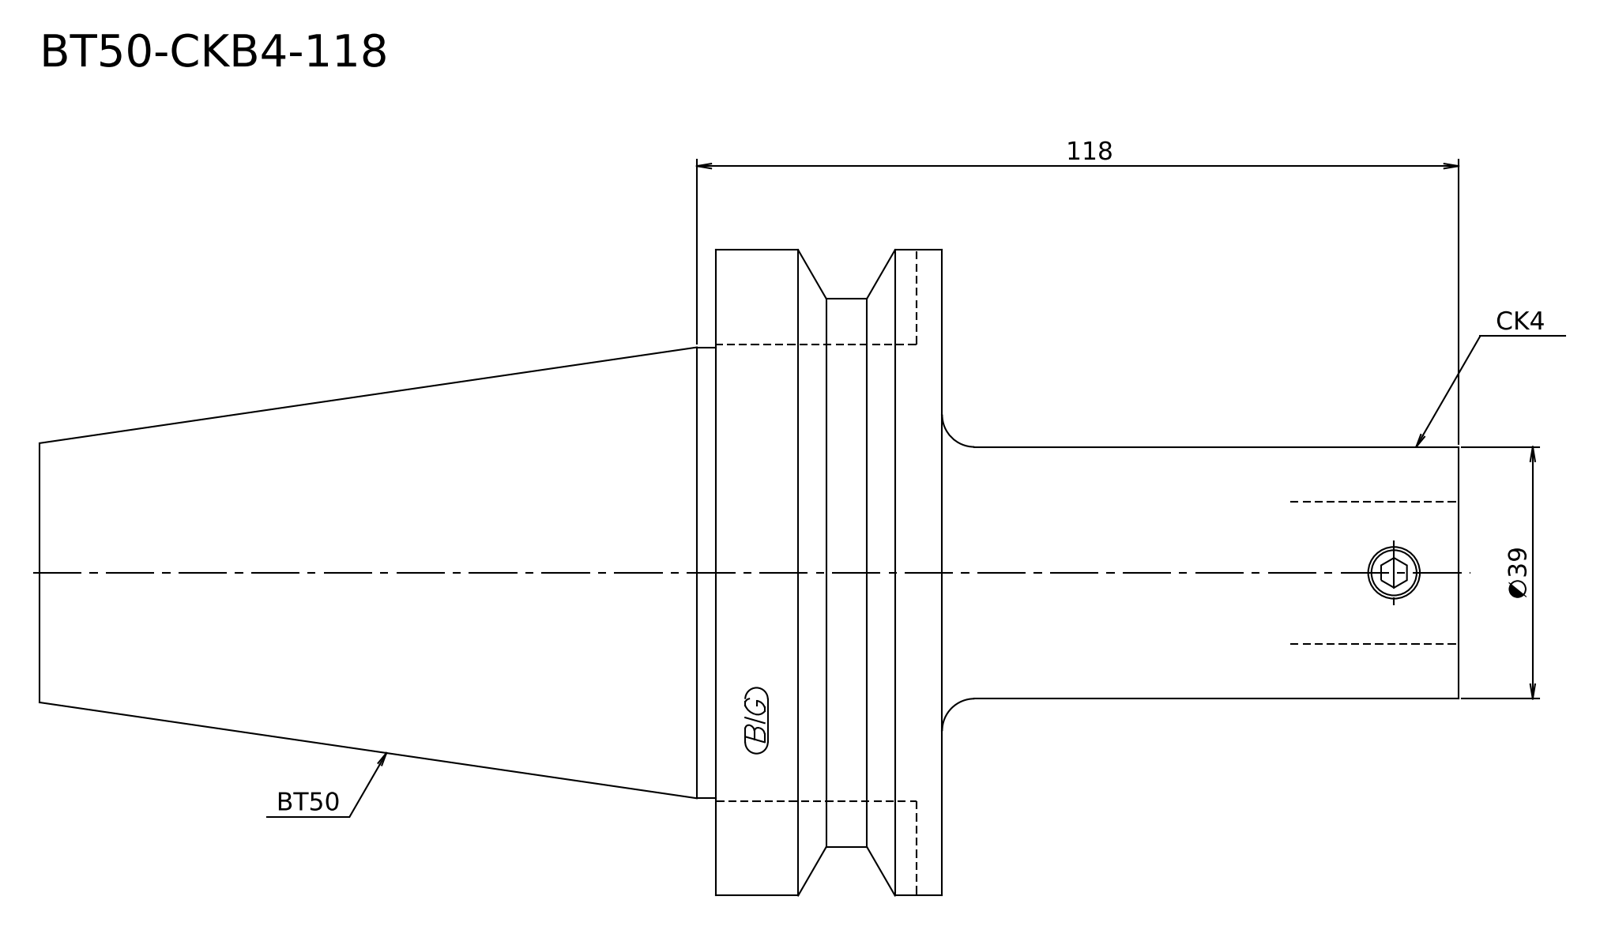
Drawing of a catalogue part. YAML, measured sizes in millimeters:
step_written_by: "Kubotek KeyCreator V8.5.1 (14335) (CONFIG_CONTROL_DESIGN)"
units: millimeters
bodies: {solids: 1, faces: 13, planar: 4, cylindrical: 5, other: 4}
overall_size: [219.8, 100, 100]
volume: 607875
surface_area: 54063
round_bosses_or_shafts:
  - {diameter: 100, count: 1}
  - {diameter: 85, count: 1}
  - {diameter: 69.85, count: 1}
  - {diameter: 39, count: 1}
face_to_face_distances: [35, 139.8, 104.8, 80, 115, 219.8]
